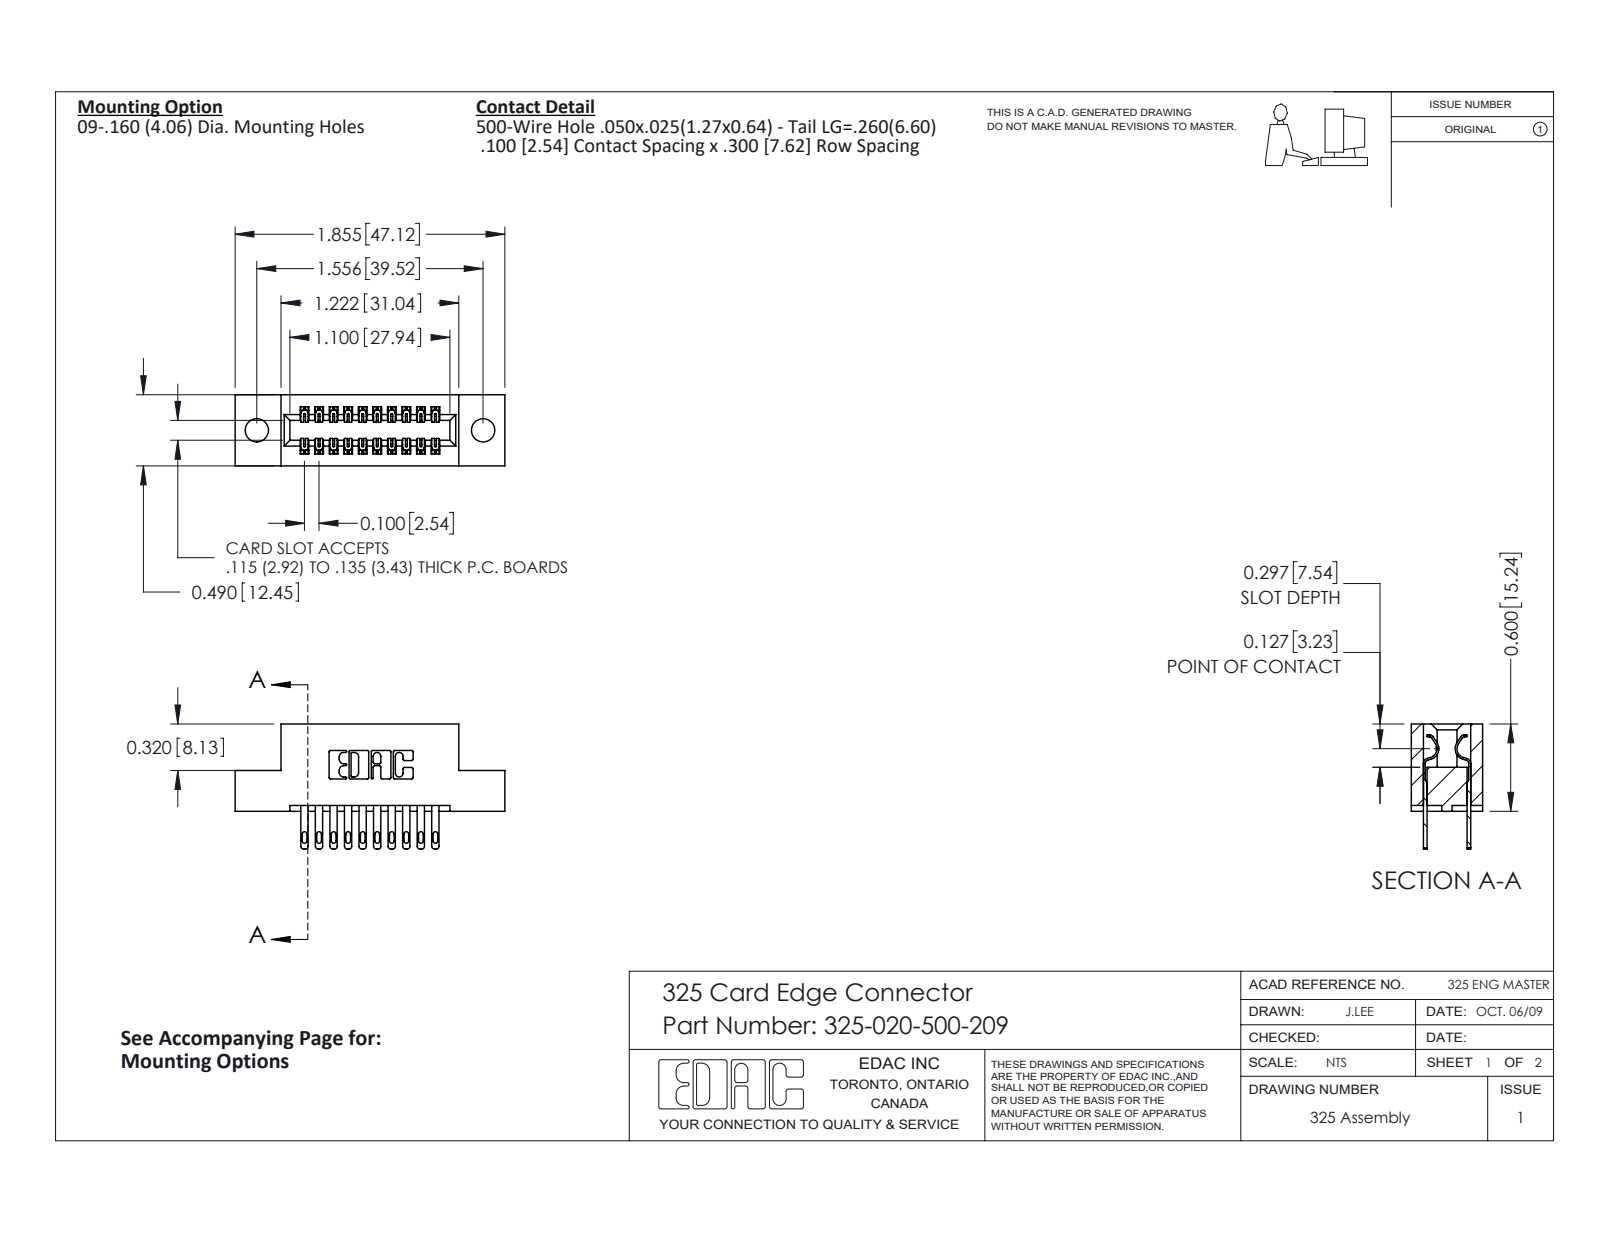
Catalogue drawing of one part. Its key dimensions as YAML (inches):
part_name: "325-292-001_325-293-100; 325 Part_.160 TH; 325-020-500-209"
step_written_by: "SolidWorks 2016 (CONFIG_CONTROL_DESIGN)"
units: inches
bodies: {solids: 21, faces: 1074, planar: 670, cylindrical: 404, other: 0}
overall_size: [1.855, 0.86, 0.49]
volume: 0.343
surface_area: 9.579
round_holes:
  - {diameter: 0.16, count: 2}
partial_cylinders:
  - {radius: 0.006, count: 30}
  - {radius: 0.01, count: 22}
  - {radius: 0.016, count: 20}
  - {radius: 0.02, count: 20}
  - {radius: 0.007, count: 6}
  - {radius: 0.031, count: 6}
  - {radius: 0.026, count: 3}
  - {radius: 0.014, count: 2}
face_to_face_distances: [0.3, 0.083, 0.407, 0.04, 0.1, 0.49, 0.107, 0.383, 0.025, 0.2]
hole_center_spacings: [1.556]
